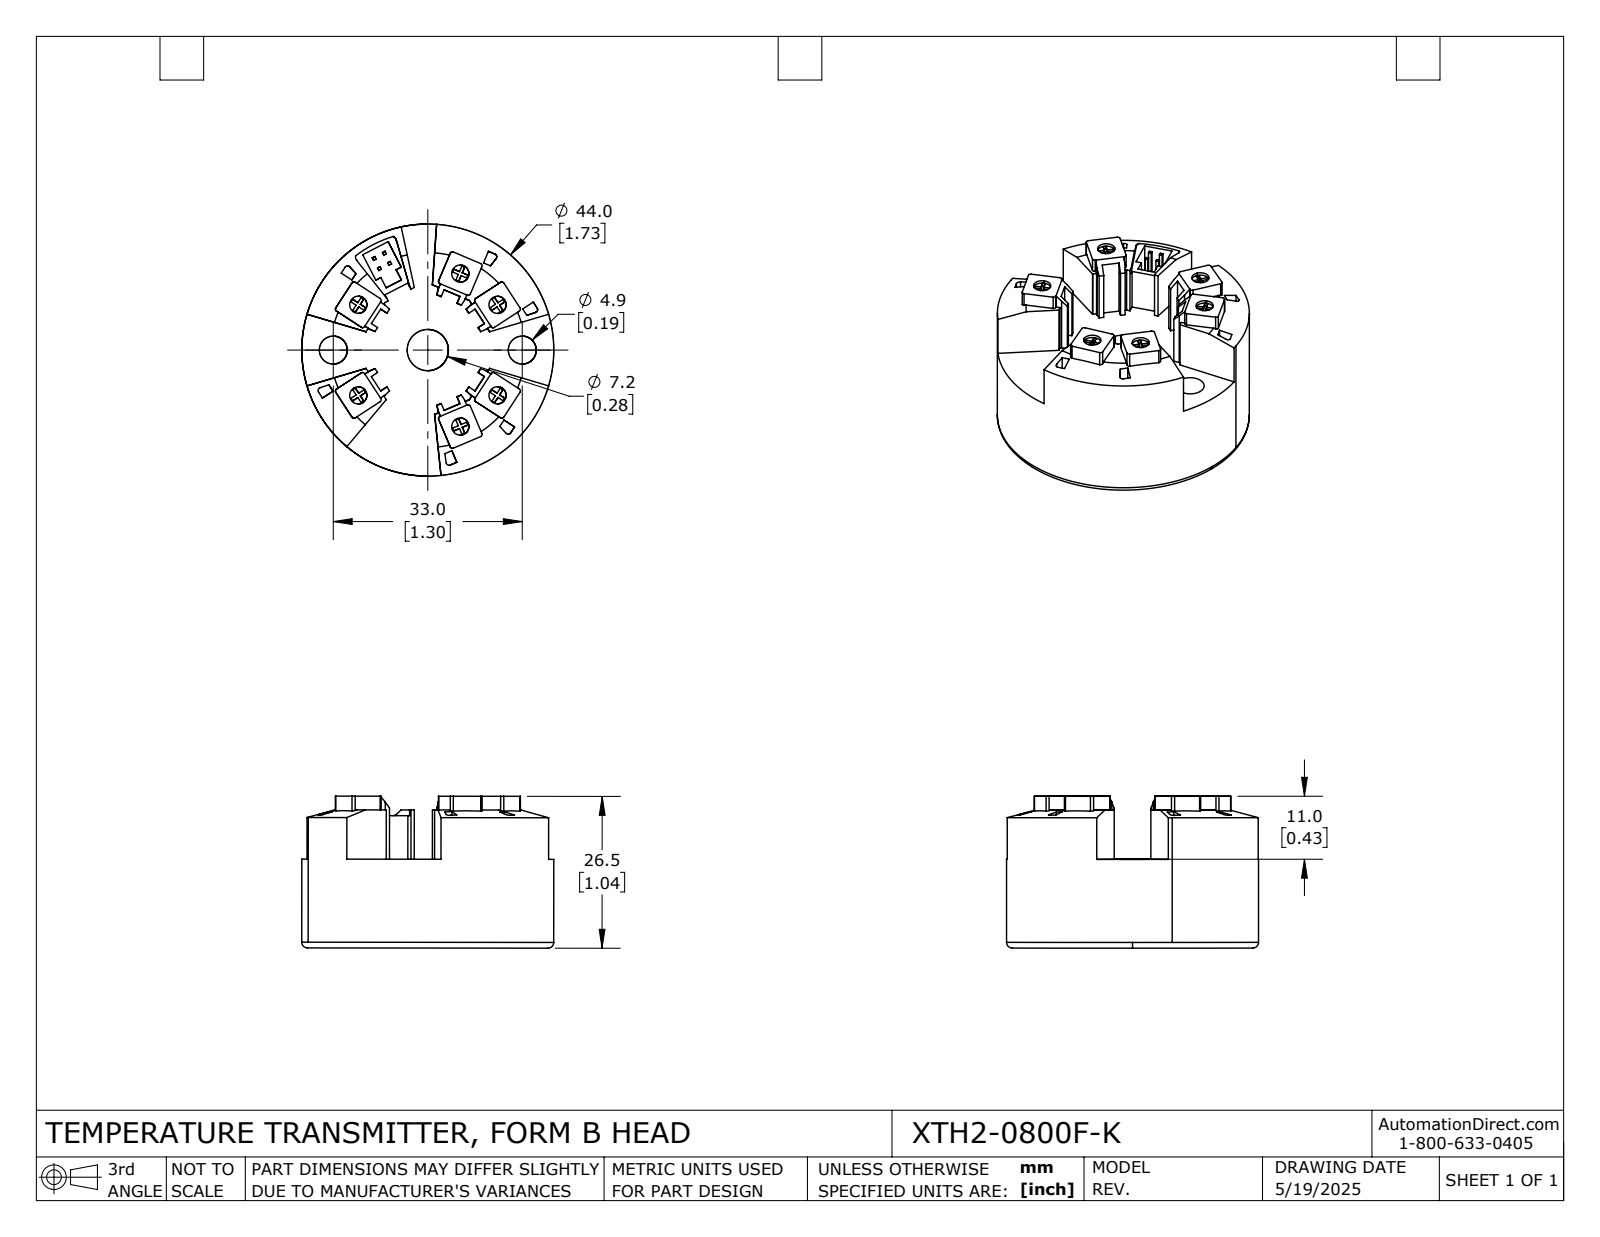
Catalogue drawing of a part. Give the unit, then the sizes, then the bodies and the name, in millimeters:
Units: millimetres
Overall size (bounding box): 44 × 44 × 26.5
Round holes (diameter × count): ⌀3 ×6, ⌀4.9 ×2, ⌀7.2 ×1
Round bosses / shafts (diameter × count): ⌀44 ×1
Partial cylindrical surfaces — rounded edges, fillets, slot ends (radius × count): R0.4 ×24, R0.5 ×6, R1 ×2
Main face-to-face distances: 15.5, 26.5, 11, 1.5, 4.5, 1, 0.5, 3, 24.1, 8.6
Hole centre spacings: 14.5, 8.5, 9, 9, 16.5, 17.2, 18.6, 22.2
Volume: 28 640 mm³ · Surface area: 8 684 mm²
Bodies: 1 solid, 341 faces (281 planar, 52 cylindrical, 8 other)
Part name (STEP PRODUCT): XTDH2-0800F-K
STEP written by: SolidWorks 2024 (AUTOMOTIVE_DESIGN)
